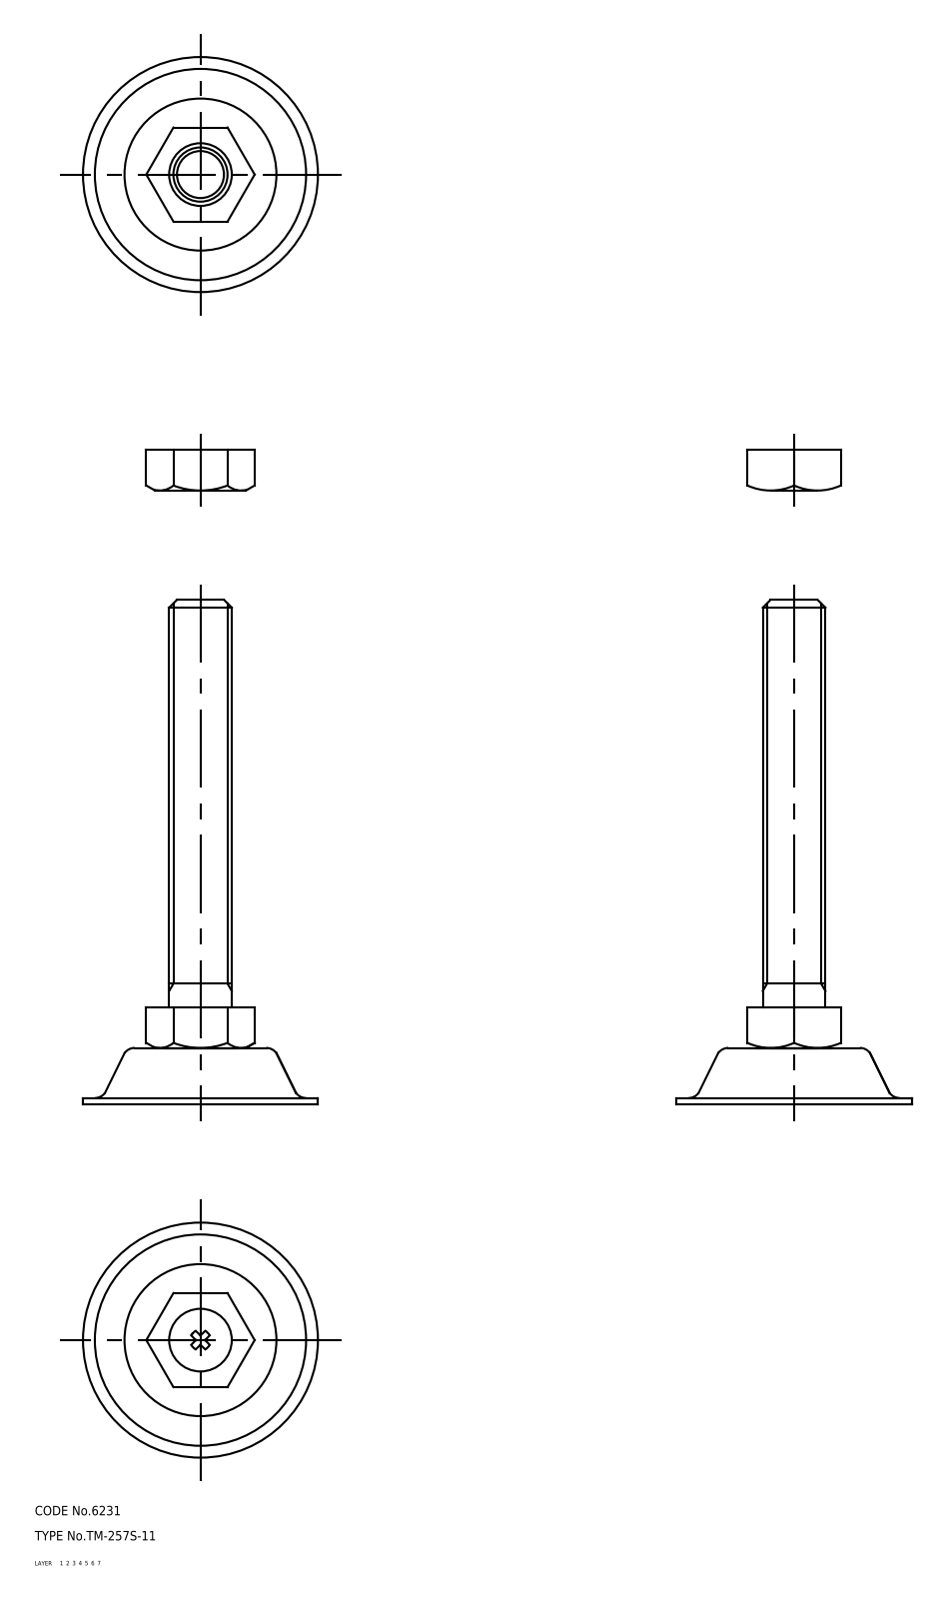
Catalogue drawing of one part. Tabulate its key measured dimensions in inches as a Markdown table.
| quantity | value |
| --- | --- |
| part name | nut; foot; bolt; TM_257S_11_10148_36 |
| STEP written by | CADfix (AUTOMOTIVE_DESIGN) |
| units | inches |
| bodies | 4 solids, 83 faces (0 planar, 0 cylindrical, 83 other) |
| overall size | 6.339 × 2.953 × 2.953 |
| volume | 4.819 in³ |
| surface area | 46.38 in² |
